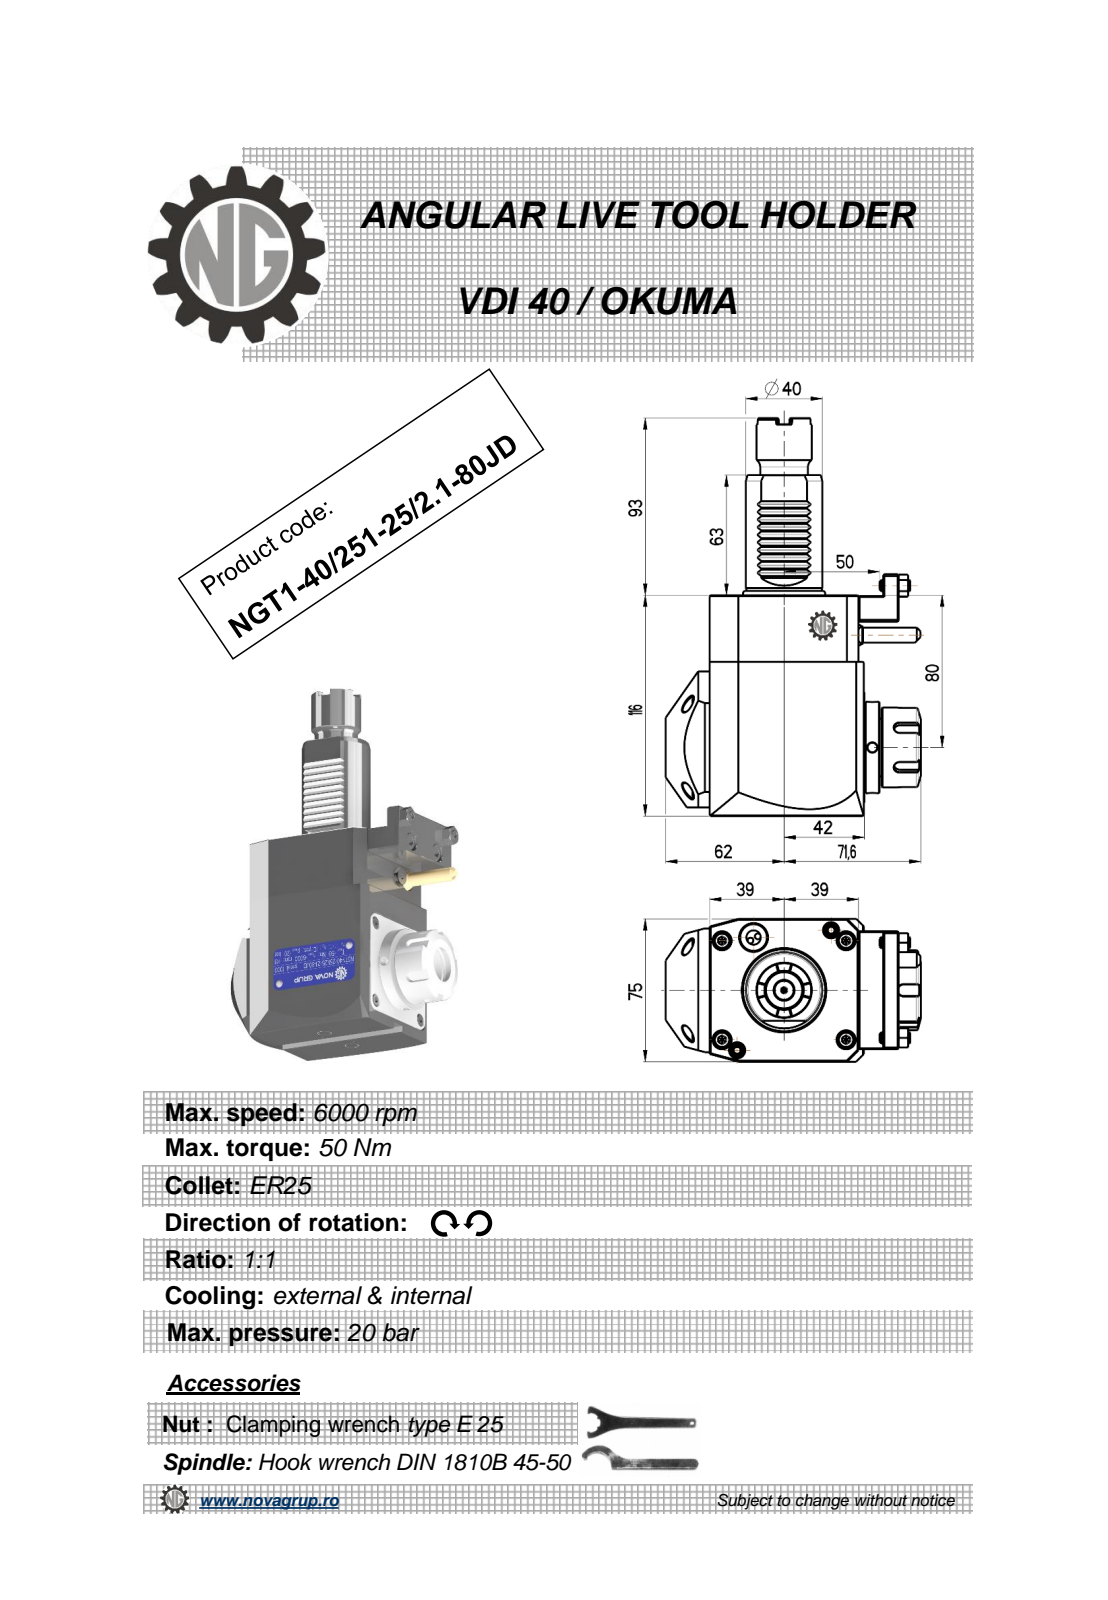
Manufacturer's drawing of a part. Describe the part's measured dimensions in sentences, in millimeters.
The part is named "NGT1_40_251_25_2_1_80JD". Its 3-D file was written by "PRO/ENGINEER BY PARAMETRIC TECHNOLOGY CORPORATION, 2010280 (CONFIG_CONTROL_DESIGN)". It is 1 solid with 479 faces: 196 planar, 86 cylindrical and 197 other. Overall it measures 209 by 133.6 by 76.6 millimeters. Its volume is 906 365 cubic millimeters and its surface area 74 662 square millimeters. Round holes: 3 of diameter 5, 1 of diameter 3, 1 of diameter 20.3. Round bosses or shafts: 2 of diameter 6, 1 of diameter 48, 1 of diameter 42, 1 of diameter 40, 1 of diameter 37.5, 1 of diameter 33, 1 of diameter 29, 1 of diameter 25. Partial cylindrical surfaces (rounded edges, fillets, slot ends): 10 of radius 0.3, 10 of radius 0.31, 6 of radius 0.2, 5 of radius 3, 1 of radius 0.5, 1 of radius 10, 1 of radius 40. The main face-to-face distances are 75, 116, 81, 0.5, 10, 21, 11, 80.8, 8, 112. The hole center spacings are 61.13.
